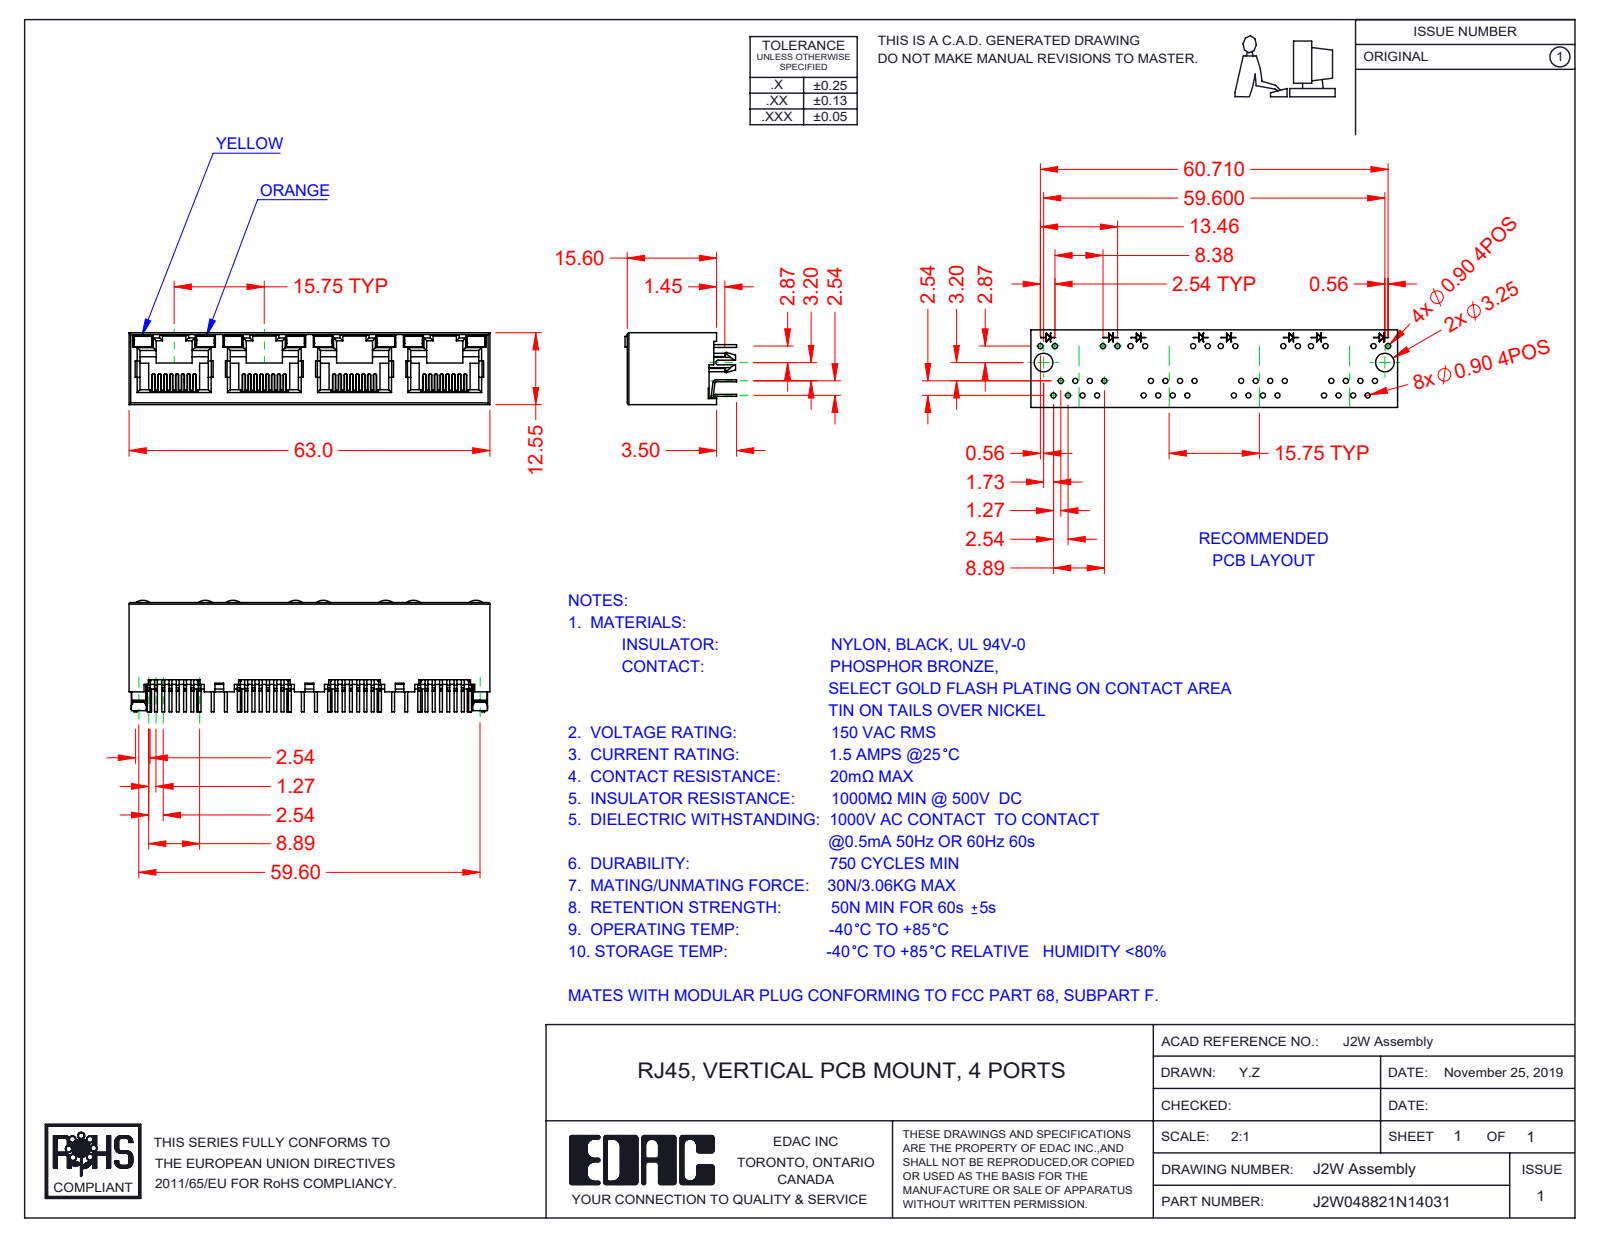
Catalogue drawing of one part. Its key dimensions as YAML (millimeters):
part_name: "2W LED RH_4-Orange; 2W LED LH_1-Yellow; 2W Insulator; J2W048821N14031 (+2 more)"
step_written_by: "SolidWorks 2020 (CONFIG_CONTROL_DESIGN)"
units: millimeters
bodies: {solids: 45, faces: 3135, planar: 2600, cylindrical: 477, other: 58}
overall_size: [63, 19.5, 12.55]
volume: 5335
surface_area: 13144
partial_cylinders:
  - {radius: 0.15, count: 64}
  - {radius: 0.2, count: 29}
  - {radius: 0.5, count: 28}
  - {radius: 0.3, count: 14}
  - {radius: 0.45, count: 8}
  - {radius: 2, count: 8}
  - {radius: 0.25, count: 2}
  - {radius: 1.5, count: 2}
face_to_face_distances: [12.55, 11.9, 0.65, 15.75, 0.36, 1.5, 0.78, 0.6, 11.3, 31.5]
